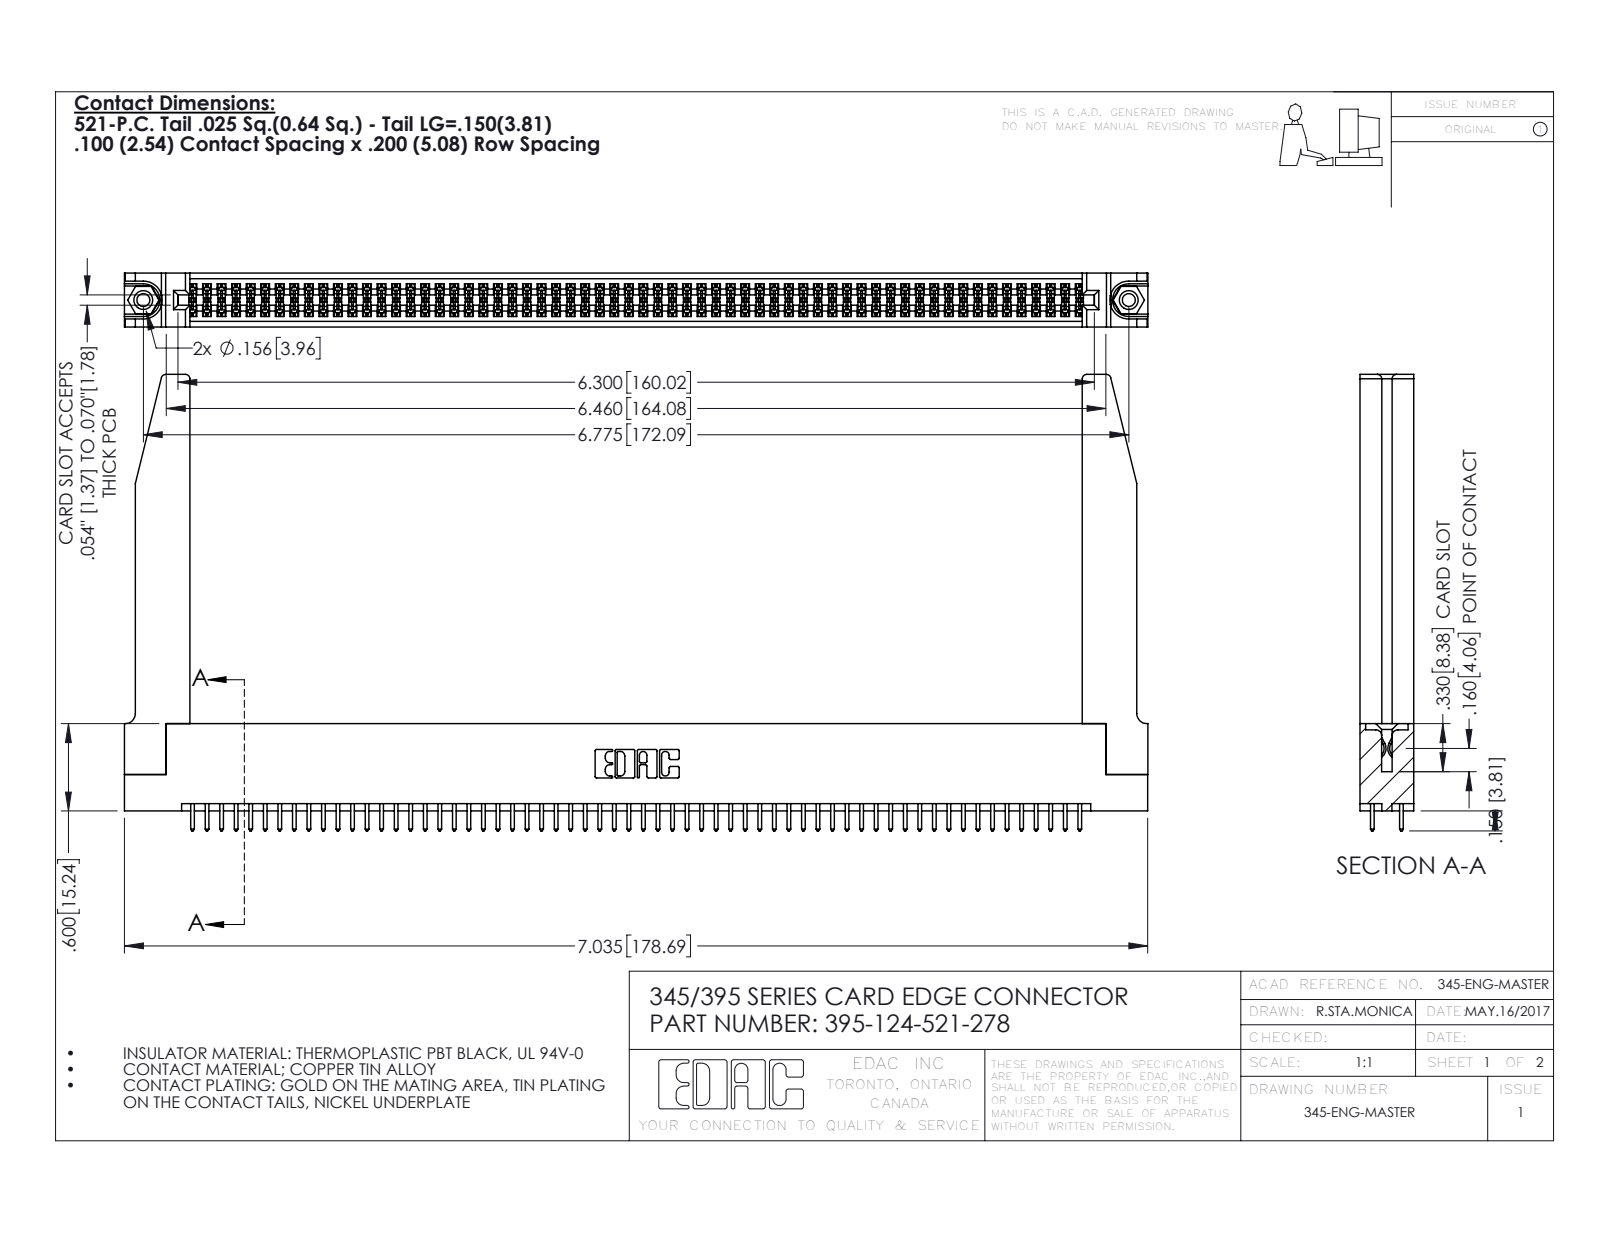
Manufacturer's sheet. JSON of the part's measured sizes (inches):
{"part_name": "345-220-078_345-220-078; 395-124-521-278; 345-292-001_345-293-121; 345 Part_Flush Mounting Lugs - 0.156 Dia-TH (+1 more)", "step_written_by": "SolidWorks 2016 (CONFIG_CONTROL_DESIGN)", "units": "inches", "bodies": {"solids": 129, "faces": 6560, "planar": 4314, "cylindrical": 2194, "other": 52}, "overall_size": [7.036, 3.137, 0.37], "volume_in3": 1.542, "surface_area_in2": 50.77, "round_holes": [[0.089, 2], [0.125, 2], [0.156, 2], [0.064, 1]], "round_bosses_or_shafts": [[0.155, 2]], "partial_cylinders_radius": [[0.006, 186], [0.01, 124], [0.01, 22], [0.03, 8], [0.007, 6], [0.031, 6], [0.026, 3], [0.014, 2]], "face_to_face_distances": [0.072, 0.298, 0.37, 0.2, 0.098, 0.272, 0.025, 0.225, 0.175, 0.148], "hole_center_spacings": [0.27, 6.539, 6.775]}
